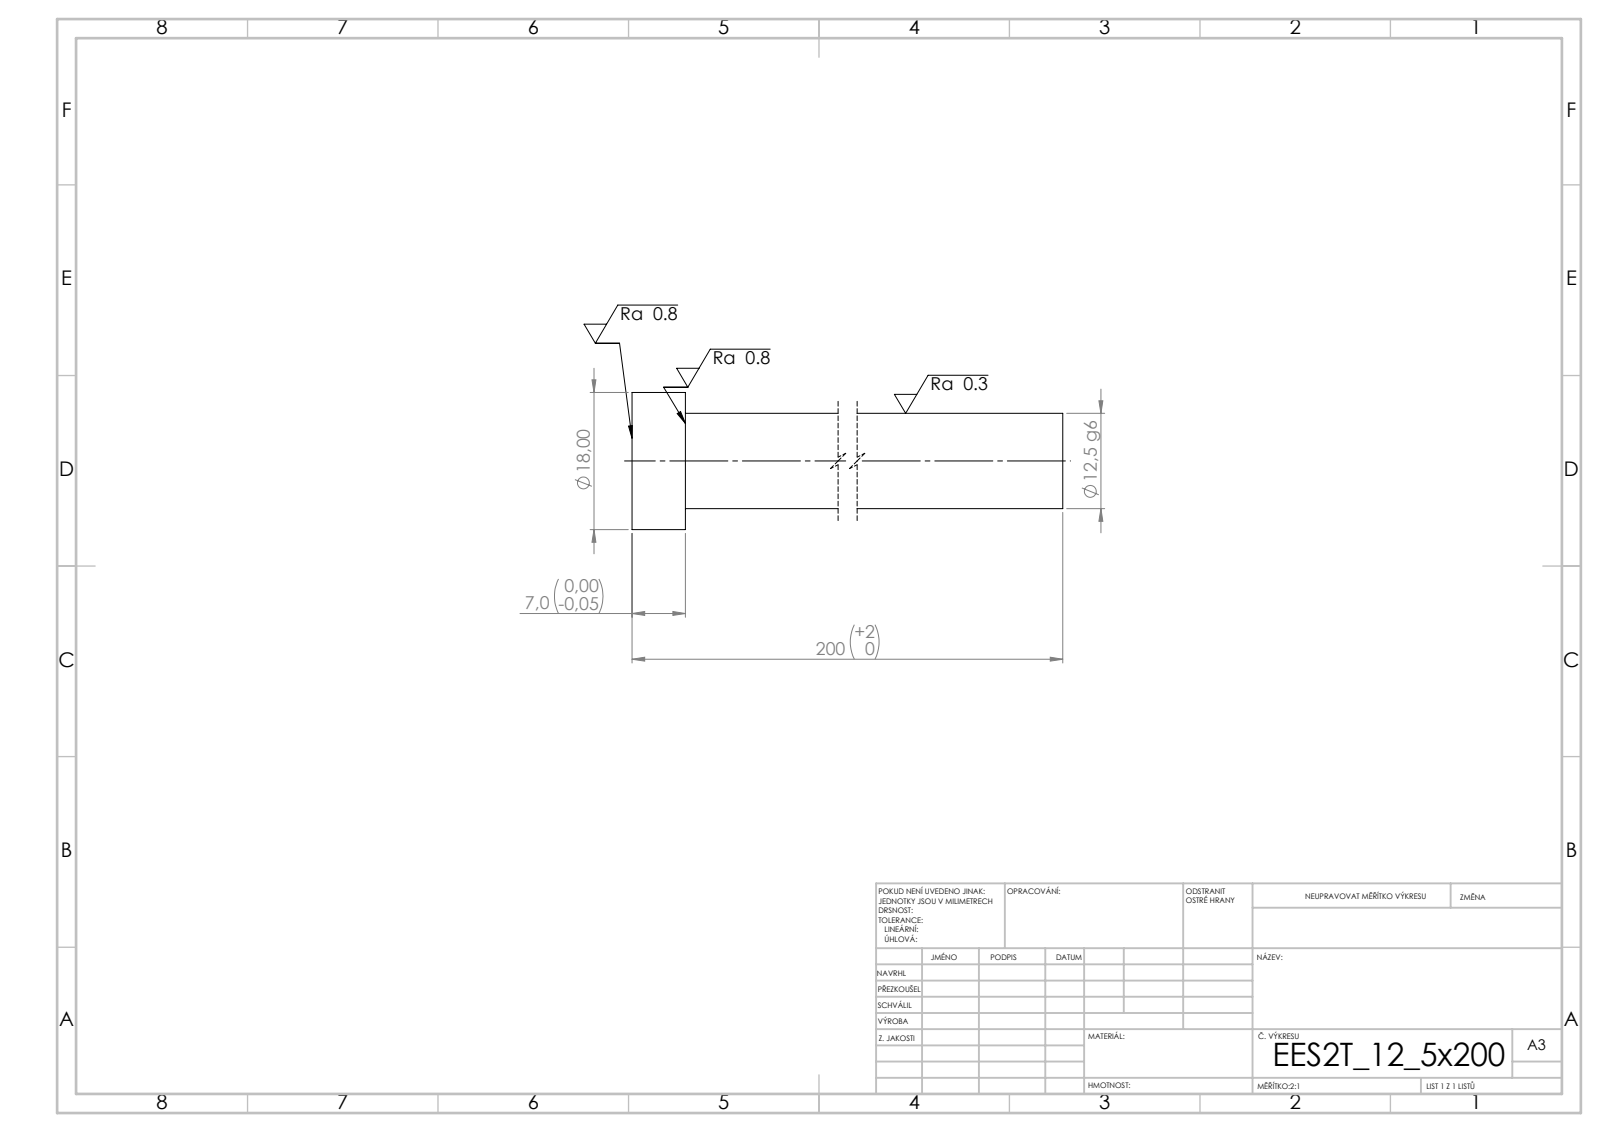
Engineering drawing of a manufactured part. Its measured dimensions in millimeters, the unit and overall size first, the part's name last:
Units: millimetres
Overall size (bounding box): 200 × 18 × 18
Round bosses / shafts (diameter × count): ⌀18 ×1, ⌀12.5 ×1
Main face-to-face distances: 7, 200, 193
Volume: 25 466 mm³ · Surface area: 8 484 mm²
Bodies: 1 solid, 7 faces (3 planar, 4 cylindrical, 0 other)
STEP written by: SolidWorks 2019 (CONFIG_CONTROL_DESIGN)
